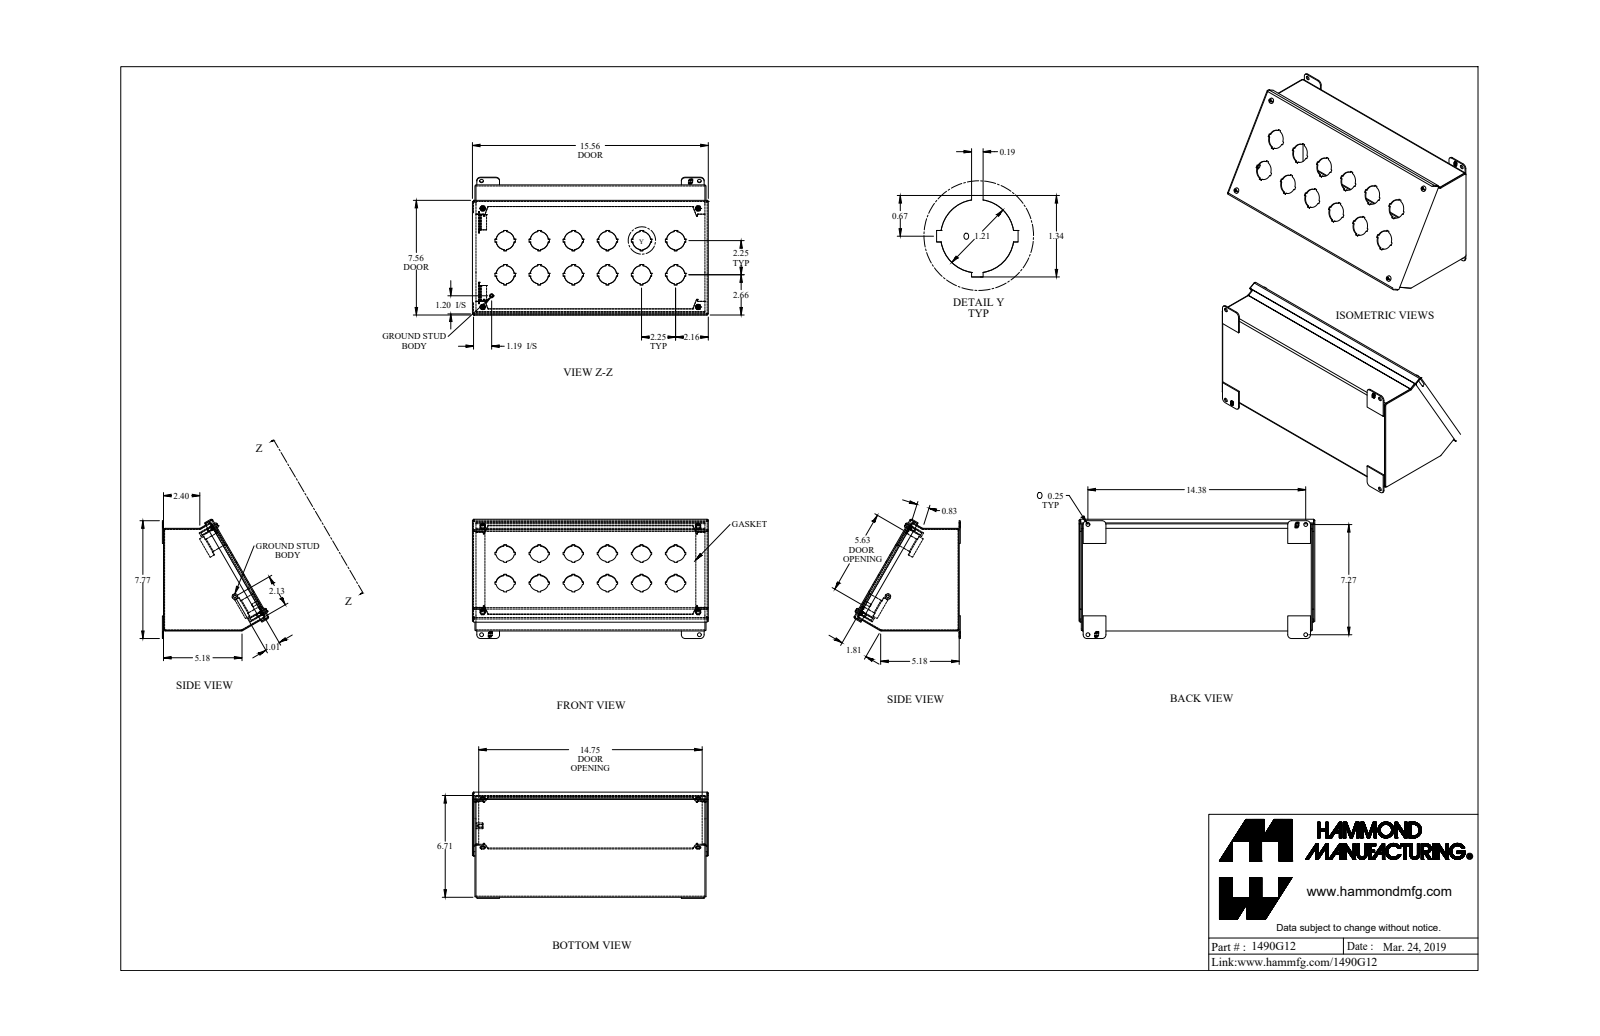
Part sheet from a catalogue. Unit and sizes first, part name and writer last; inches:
Units: inches
Overall size (bounding box): 15.562 × 7.869 × 7.008
Round holes (diameter × count): ⌀1.21 ×12, ⌀0.25 ×8, ⌀0.159 ×4, ⌀0.156 ×1
Round bosses / shafts (diameter × count): ⌀0.39 ×4, ⌀0.275 ×4, ⌀0.19 ×4, ⌀0.148 ×4, ⌀0.375 ×1, ⌀0.25 ×1, ⌀0.188 ×1
Partial cylindrical surfaces — rounded edges, fillets, slot ends (radius × count): R0.108 ×18, R0.036 ×12, R0.25 ×8, R0.029 ×7, R0.086 ×7, R0.125 ×4, R0.16 ×4, R0.171 ×4
Main face-to-face distances: 0.072, 6.698, 0.072, 15.106, 6.77, 6.626, 15.178, 15.178, 15.25, 0.259
Hole centre spacings: 2.25, 3.182, 4.5, 5.031, 6.75, 7.115, 4.293, 6.346
Volume: 39.85 in³ · Surface area: 1 045 in²
Bodies: 28 solids, 901 faces (649 planar, 212 cylindrical, 40 other)
Part name (STEP PRODUCT): 1490G12_Default
STEP written by: SolidWorks 2019 (CONFIG_CONTROL_DESIGN)
